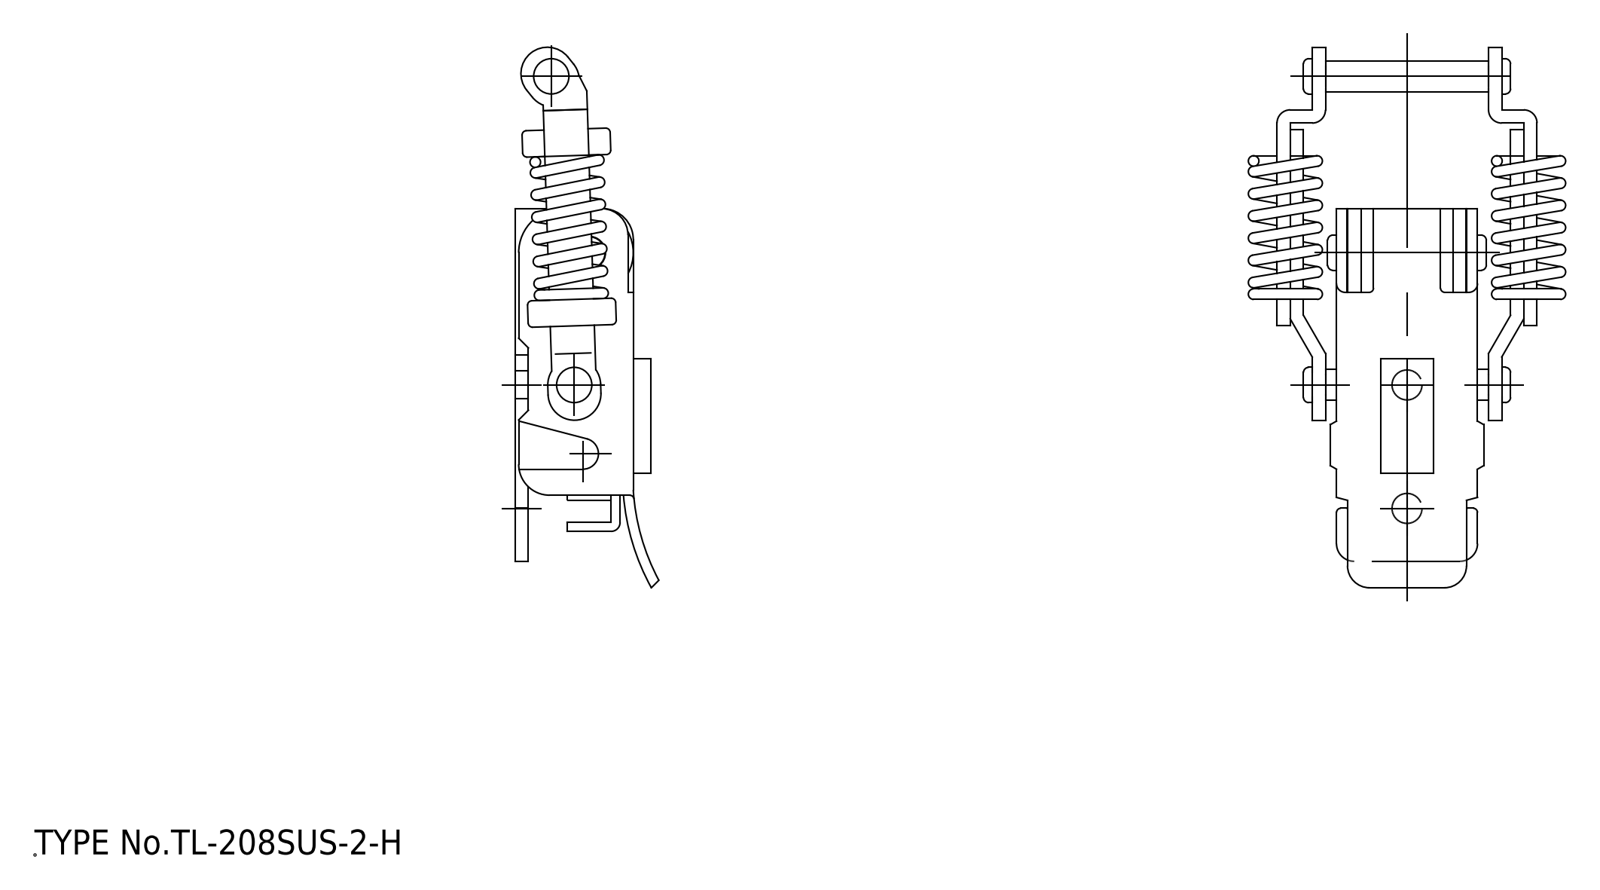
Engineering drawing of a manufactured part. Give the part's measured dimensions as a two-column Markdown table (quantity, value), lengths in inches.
| quantity | value |
| --- | --- |
| part name | アーム(A); アーム(B); ベース; レバー(A) (+2 more) |
| STEP written by | spGate 20.6.3 (****-****-****-****) (AUTOMOTIVE_DESIGN) |
| units | inches |
| bodies | 7 solids, 386 faces (195 planar, 145 cylindrical, 46 other) |
| overall size | 2.413 × 1.374 × 0.642 |
| volume | 0.34 in³ |
| surface area | 15.94 in² |
| round holes (diameter × count) | 0.134 × 2, 0.146 × 1, 0.157 × 1 |
| round bosses / shafts (diameter × count) | 0.138 × 3, 0.157 × 2, 0.098 × 1 |
| partial cylindrical surfaces (radius × count) | 0.02 × 26, 0.039 × 5, 0.118 × 5, 0.047 × 4, 0.059 × 4, 0.079 × 3, 0.138 × 3, 0.051 × 2 |
| main face-to-face distances | 0.059, 0.047, 0.118, 0.469, 0.165, 0.726, 0.317, 0.583, 0.11, 0.52 |
| hole center spacings | 0.551, 0.594 |
